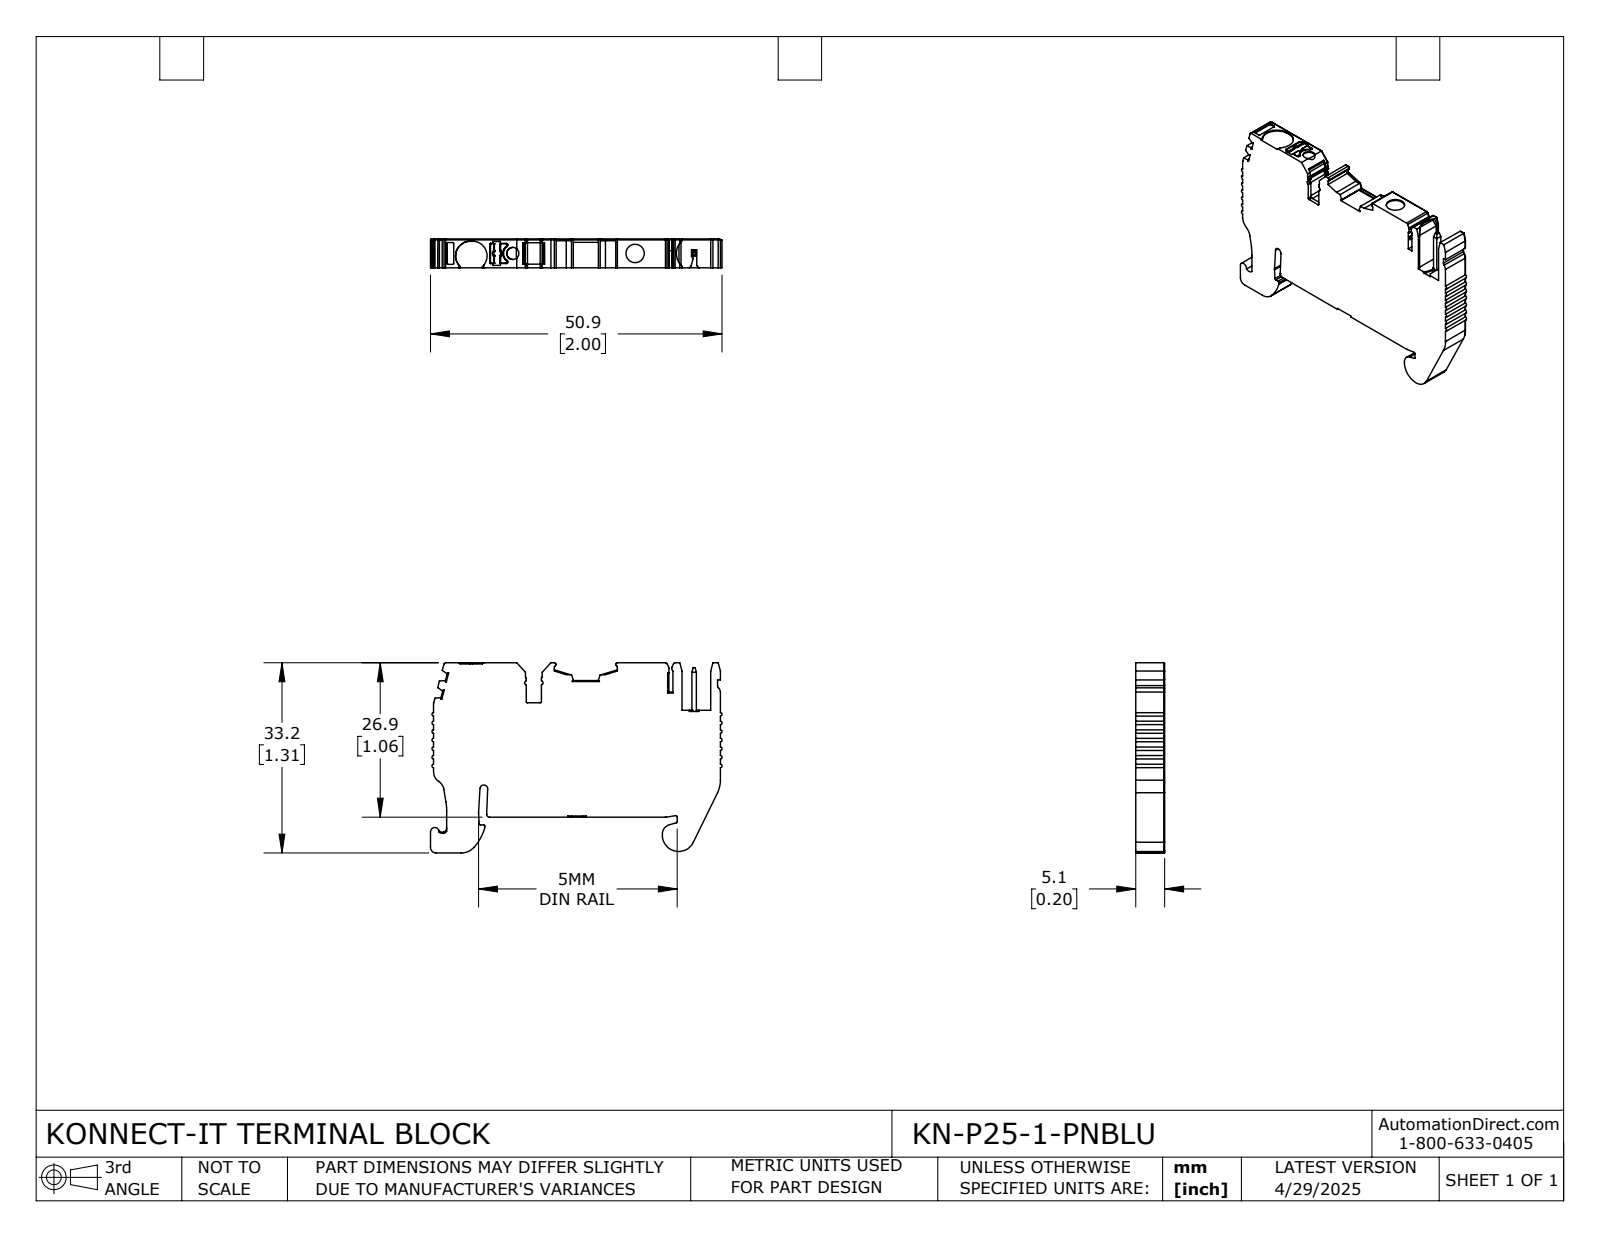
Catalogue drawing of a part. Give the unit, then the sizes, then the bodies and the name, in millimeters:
Units: millimetres
Overall size (bounding box): 50.92 × 33.21 × 5.05
Round holes (diameter × count): ⌀2.1 ×1, ⌀3.2 ×1
Partial cylindrical surfaces — rounded edges, fillets, slot ends (radius × count): R0.3 ×35, R0.2 ×34, R0.5 ×13, R0.1 ×9, R0.4 ×8, R0.15 ×4, R0.6 ×3, R0.9 ×3
Main face-to-face distances: 5.05, 26.95, 26.75, 50.08, 48.39, 1.69, 24.91, 5.2, 43.19, 6.89
Hole centre spacings: 21.35
Volume: 6 509 mm³ · Surface area: 3 879 mm²
Bodies: 1 solid, 461 faces (263 planar, 179 cylindrical, 19 other)
Part name (STEP PRODUCT): KN-P25-1-PNBLU
STEP written by: SolidWorks 2024 (CONFIG_CONTROL_DESIGN)
